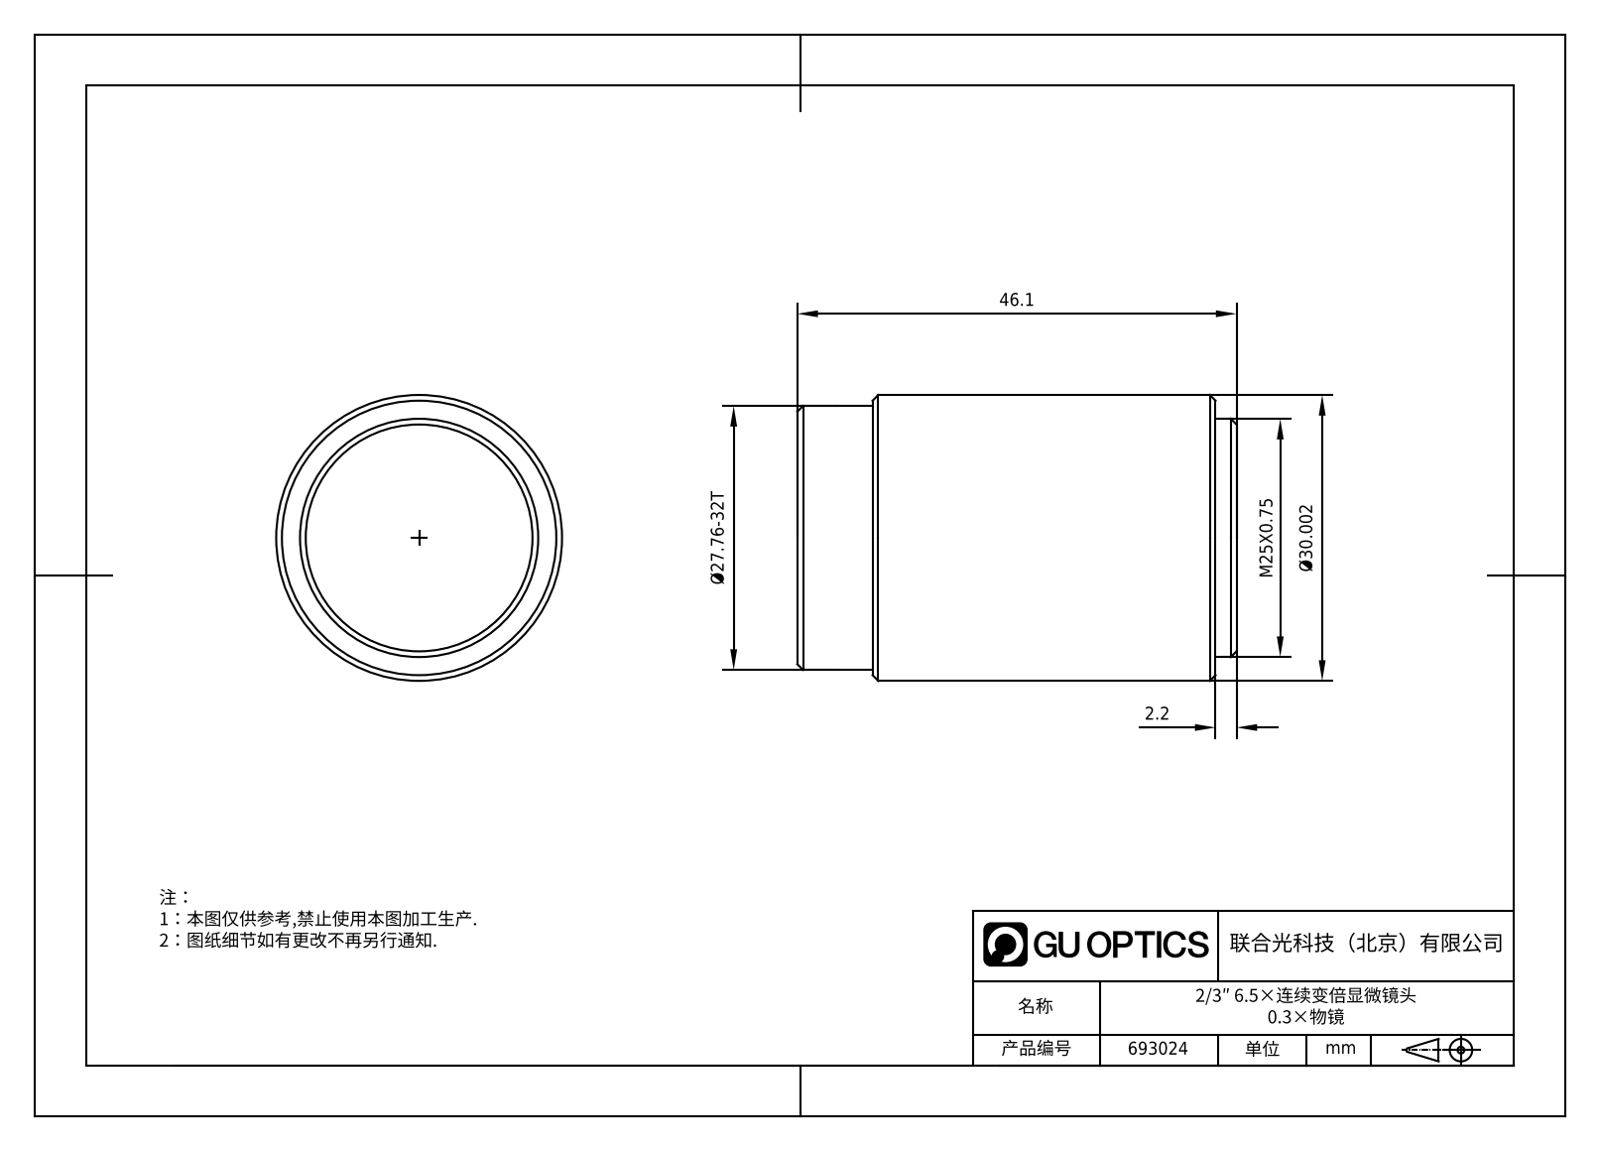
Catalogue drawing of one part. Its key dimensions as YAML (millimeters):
part_name: "66130"
step_written_by: "SolidWorks 2015 (CONFIG_CONTROL_DESIGN)"
units: millimeters
bodies: {solids: 1, faces: 18, planar: 4, cylindrical: 6, other: 8}
overall_size: [46.1, 30, 30]
volume: 31225
surface_area: 5541
round_bosses_or_shafts:
  - {diameter: 30, count: 1}
  - {diameter: 27.7, count: 1}
  - {diameter: 25, count: 1}
face_to_face_distances: [46.1, 43.9, 2.2, 7.9, 36, 38.2]
